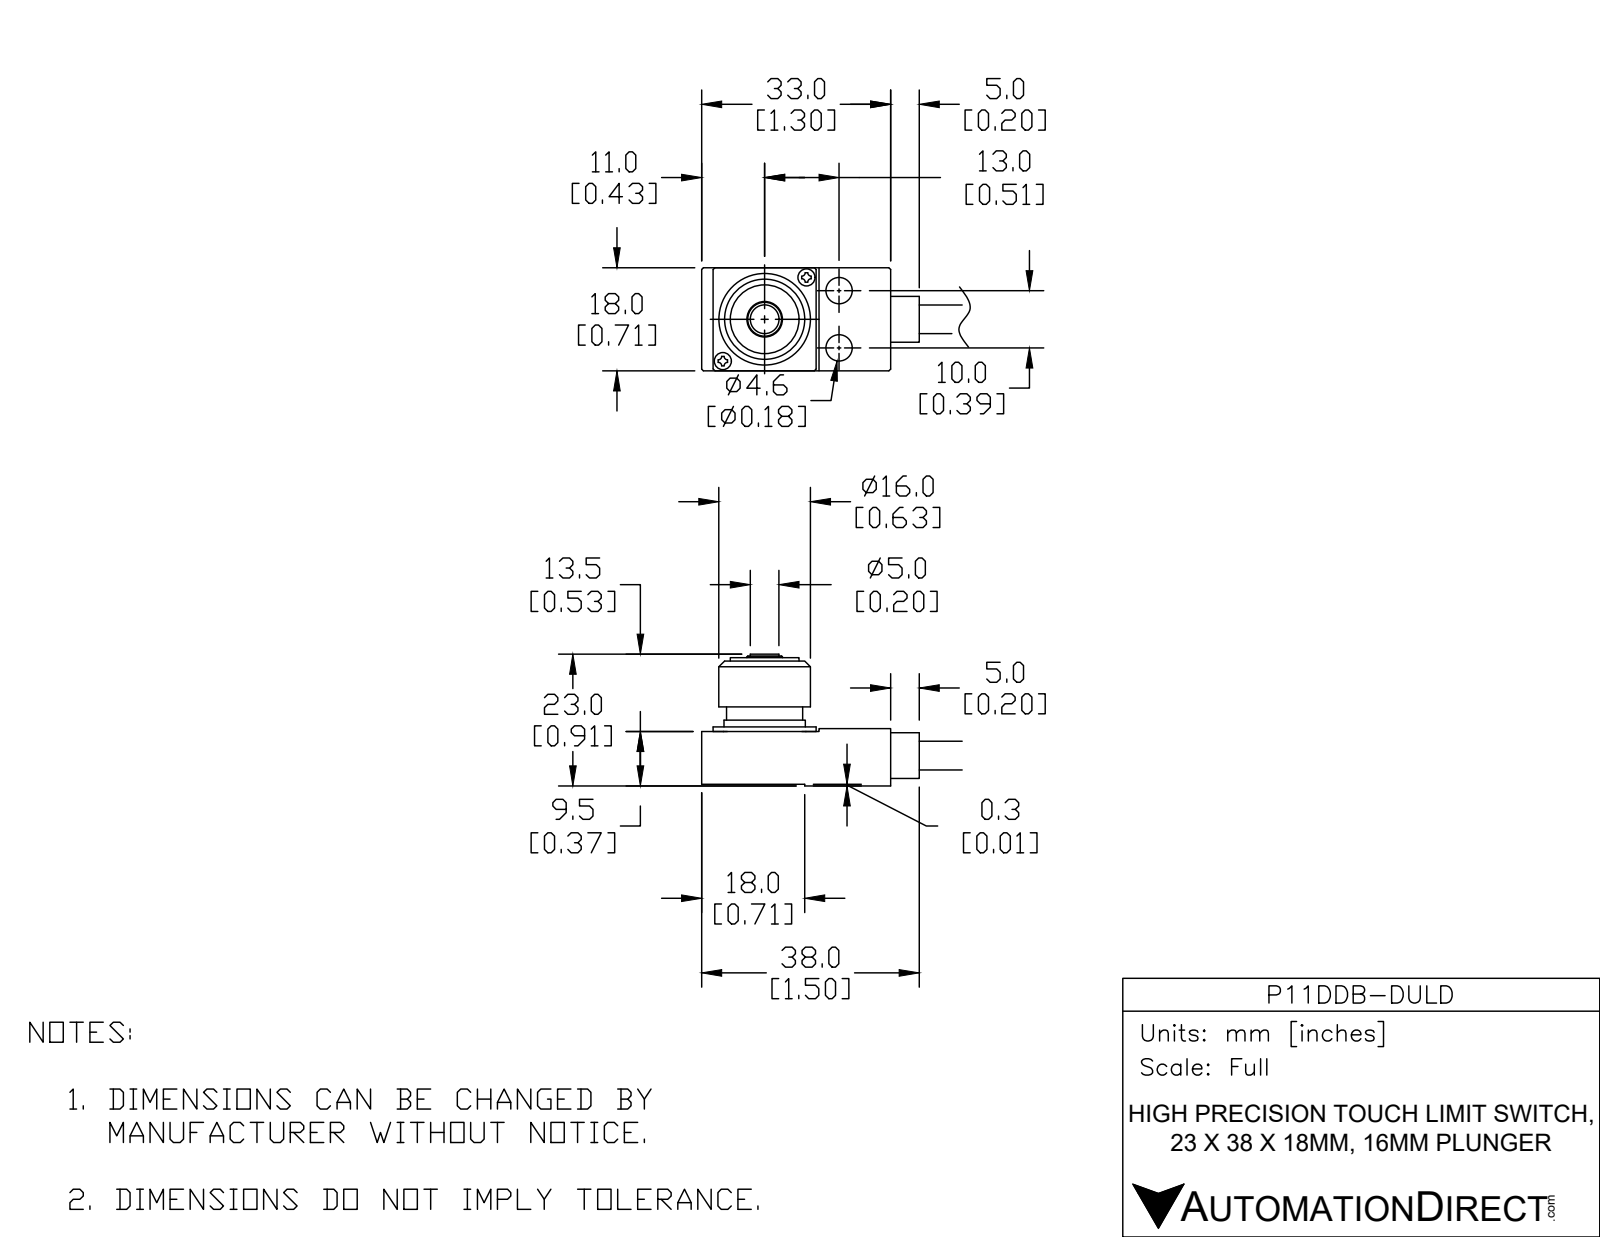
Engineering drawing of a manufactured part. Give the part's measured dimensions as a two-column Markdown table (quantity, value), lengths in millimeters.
| quantity | value |
| --- | --- |
| part name | P11DDB-DU |
| STEP written by | SolidWorks 2016 (CONFIG_CONTROL_DESIGN) |
| units | millimeters |
| bodies | 1 solid, 101 faces (41 planar, 44 cylindrical, 16 other) |
| overall size | 45.5 × 23 × 18 |
| volume | 8 127 mm³ |
| surface area | 3 469 mm² |
| round holes (diameter × count) | 3.2 × 2, 4.6 × 2 |
| round bosses / shafts (diameter × count) | 5 × 2, 3 × 2, 16 × 1, 14.2 × 1, 13.3 × 1, 12 × 1, 8 × 1, 6.2 × 1 |
| partial cylindrical surfaces (radius × count) | 12.5 × 1 |
| main face-to-face distances | 18, 10, 9.7, 10.3, 33, 22.4, 12.4, 22.1, 12.1, 13.5 |
| hole center spacings | 6.15, 10, 13.56, 20.43, 20.65, 23.74 |
